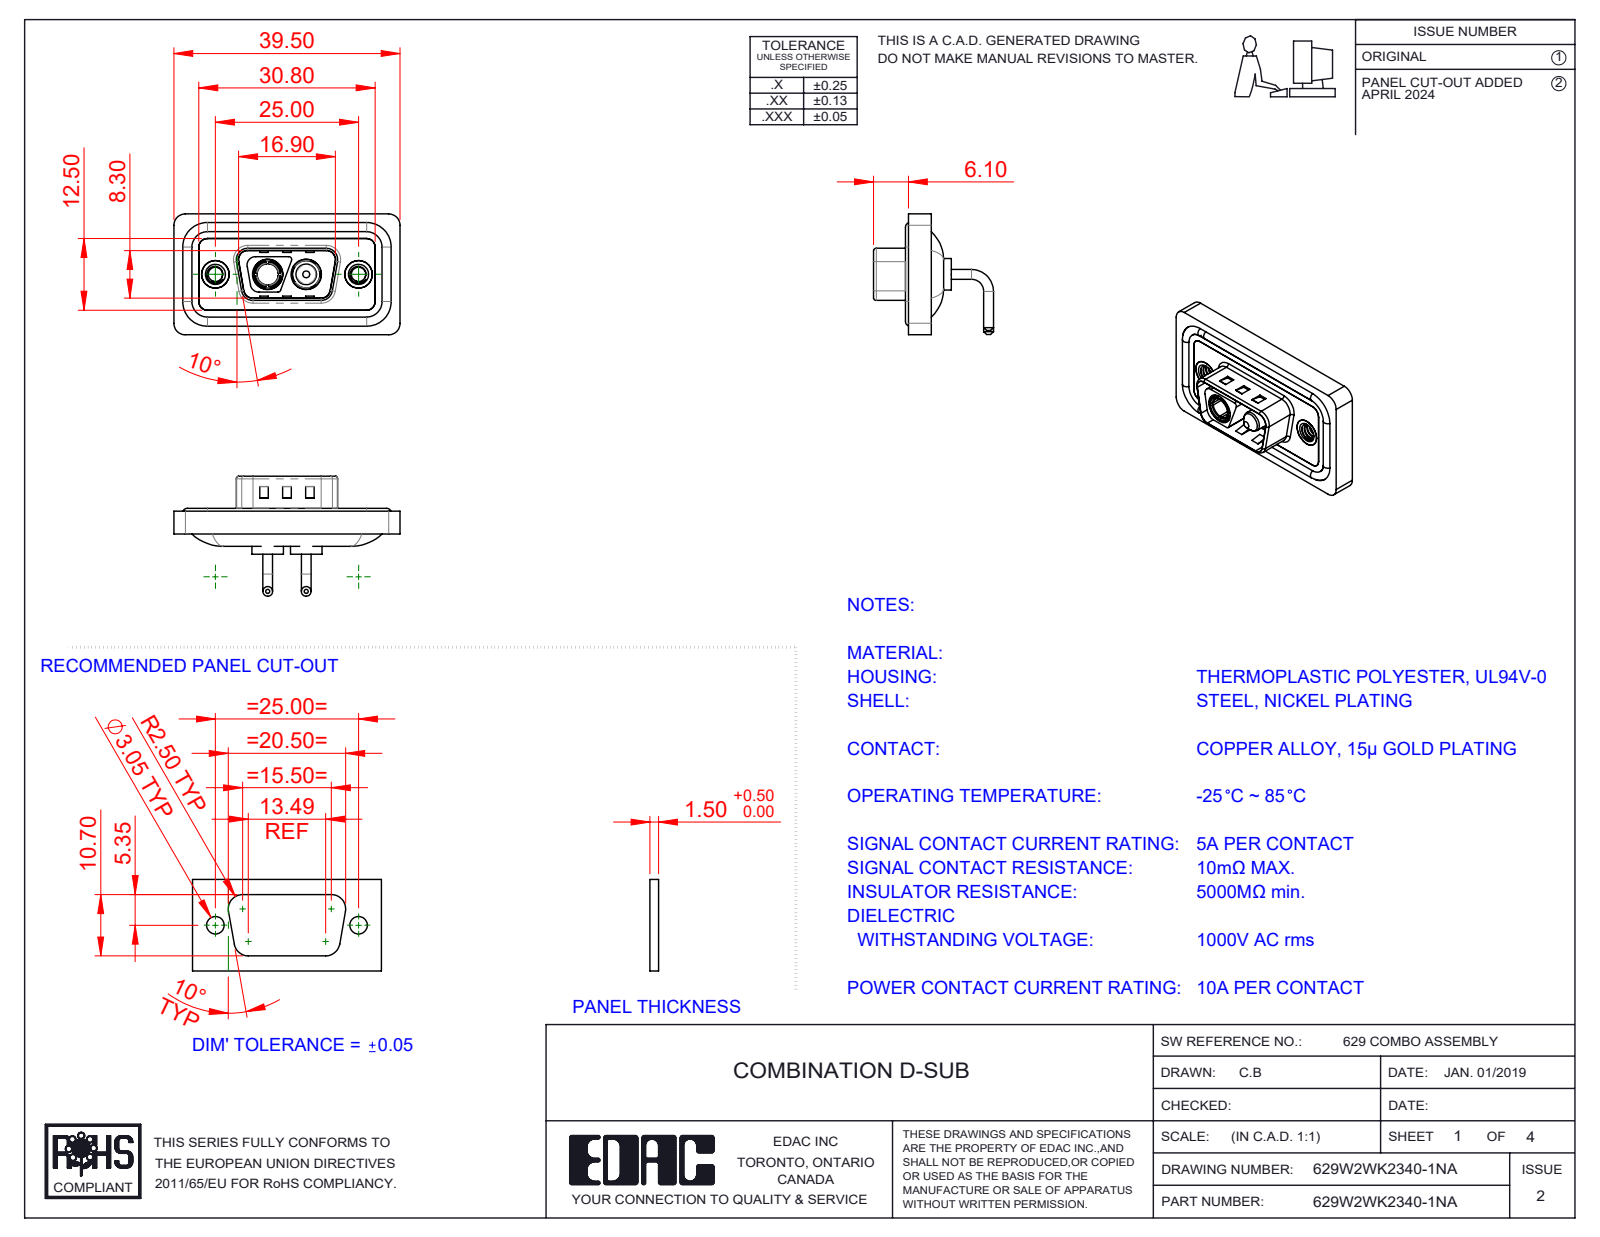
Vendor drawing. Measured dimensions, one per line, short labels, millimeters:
name: 629Combo Shell Front_09 Contacts; Power Socket_10A RA; 629W2WK2340-1NA; 629Combo Shell Rear_09 Contacts (+4 more)
written by: SolidWorks 2023 (CONFIG_CONTROL_DESIGN)
unit: mm
bodies: 11 solids, 536 faces (189 planar, 229 cylindrical, 118 other)
size: 39.5 × 21.1 × 20.95
volume: 4 567 mm³; area: 7 431 mm²
holes: 2× ⌀2.5, 2× ⌀4, 2× ⌀4.8, 2× ⌀4.85, 2× ⌀5, 2× ⌀5.3, 1× ⌀3.7
bosses: 4× ⌀1.7, 4× ⌀1.6, 2× ⌀5.5, 2× ⌀5.2, 2× ⌀4.9, 2× ⌀4.75, 2× ⌀3.75, 1× ⌀4.96
rounds: 20× R1.5, 18× R2, 10× R0.5, 8× R1.6, 4× R0.25, 4× R0.6, 4× R0.65, 4× R0.9
face distances: 0.4, 2.9, 1.1, 0.8, 2.1, 2.5, 3.1, 1.6, 4.5, 1.5
hole spacings: 9.14, 15.86, 6.72, 25
